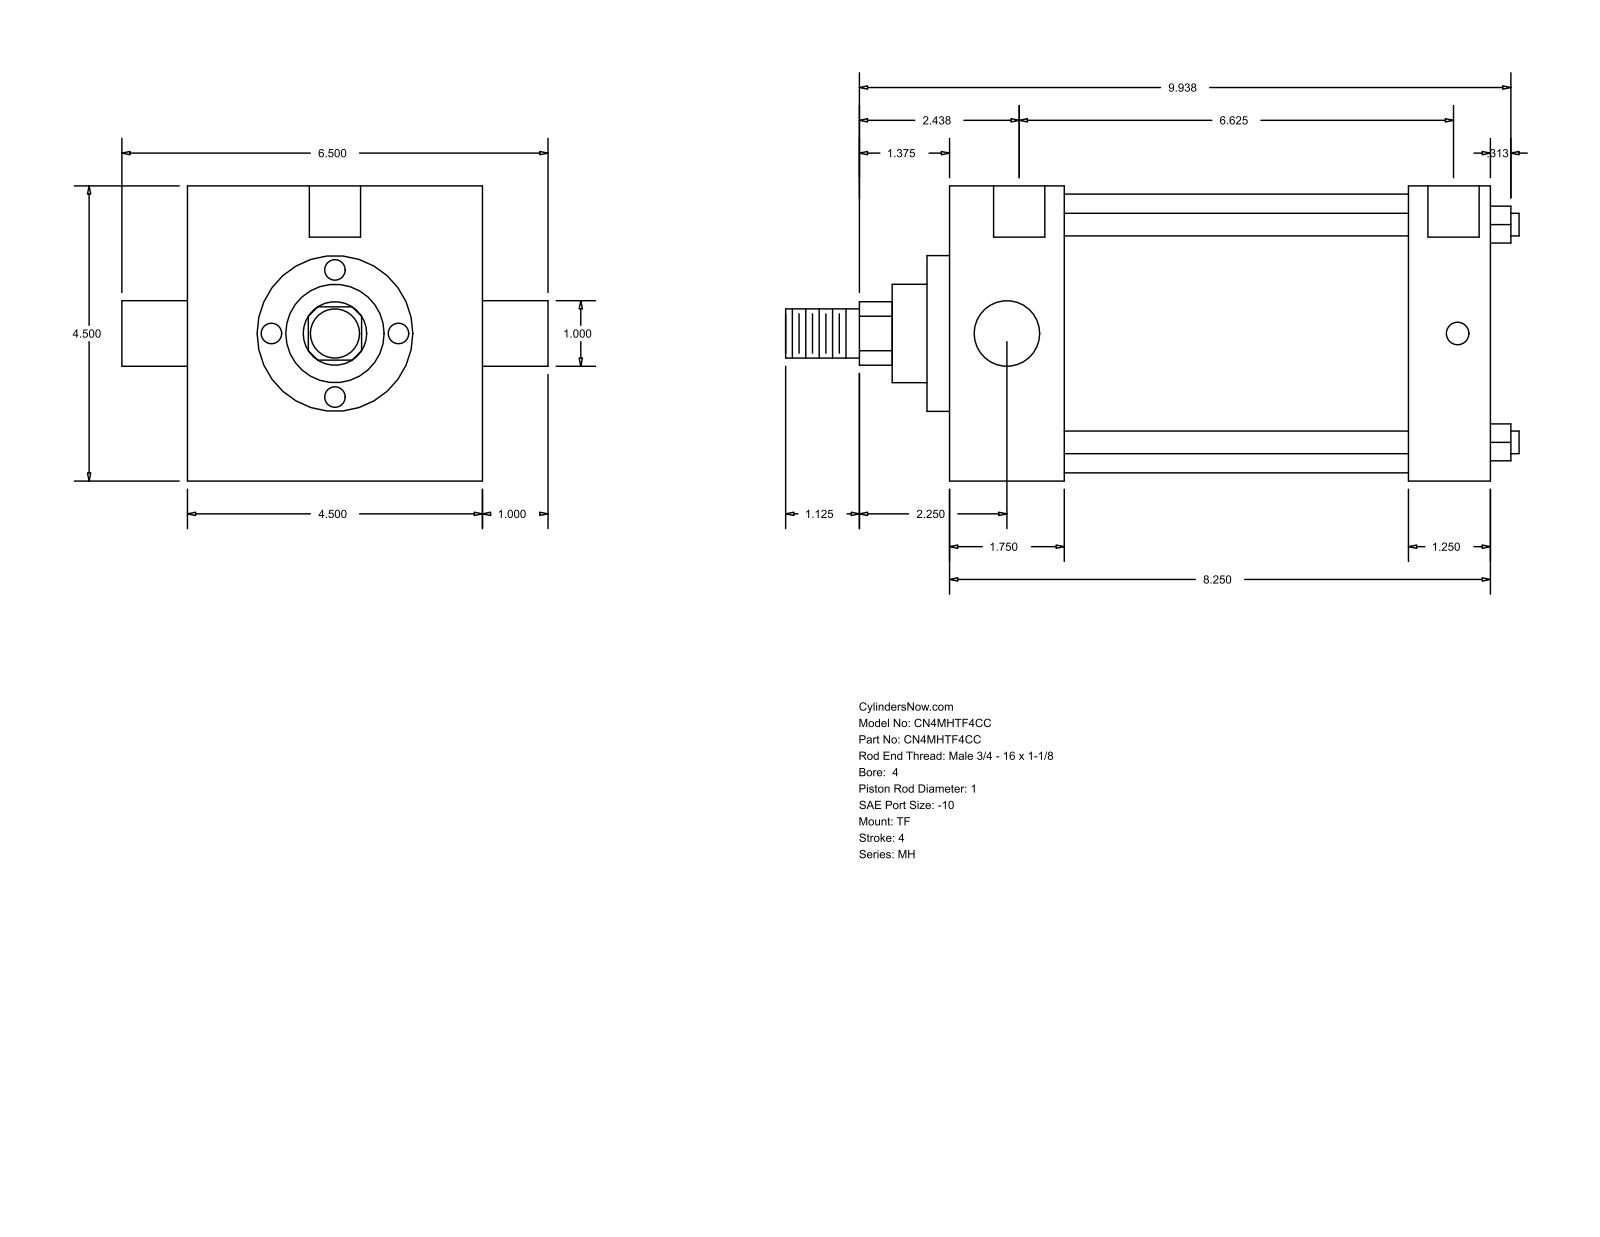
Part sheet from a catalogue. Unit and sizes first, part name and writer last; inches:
Units: inches
Overall size (bounding box): 11.187 × 6.5 × 4.5
Round holes (diameter × count): ⌀0.344 ×3, ⌀0.781 ×2
Round bosses / shafts (diameter × count): ⌀0.345 ×4, ⌀1 ×2, ⌀4.25 ×1, ⌀2.375 ×1, ⌀1.5 ×1, ⌀0.75 ×1
Partial cylindrical surfaces — rounded edges, fillets, slot ends (radius × count): R0.484 ×1
Main face-to-face distances: 4.5, 8.25, 1.75, 6.5, 7, 5.25, 1.25, 0.344, 2.094, 7.344
Hole centre spacings: 0.062, 0.063, 6.625, 6.687, 6.688, 6.75
Bodies: 0 solids, 86 faces (61 planar, 25 cylindrical, 0 other)
Part name (STEP PRODUCT): MH_TF__0400_1
STEP written by: GSSL Pune (CONFIG_CONTROL_DESIGN)
